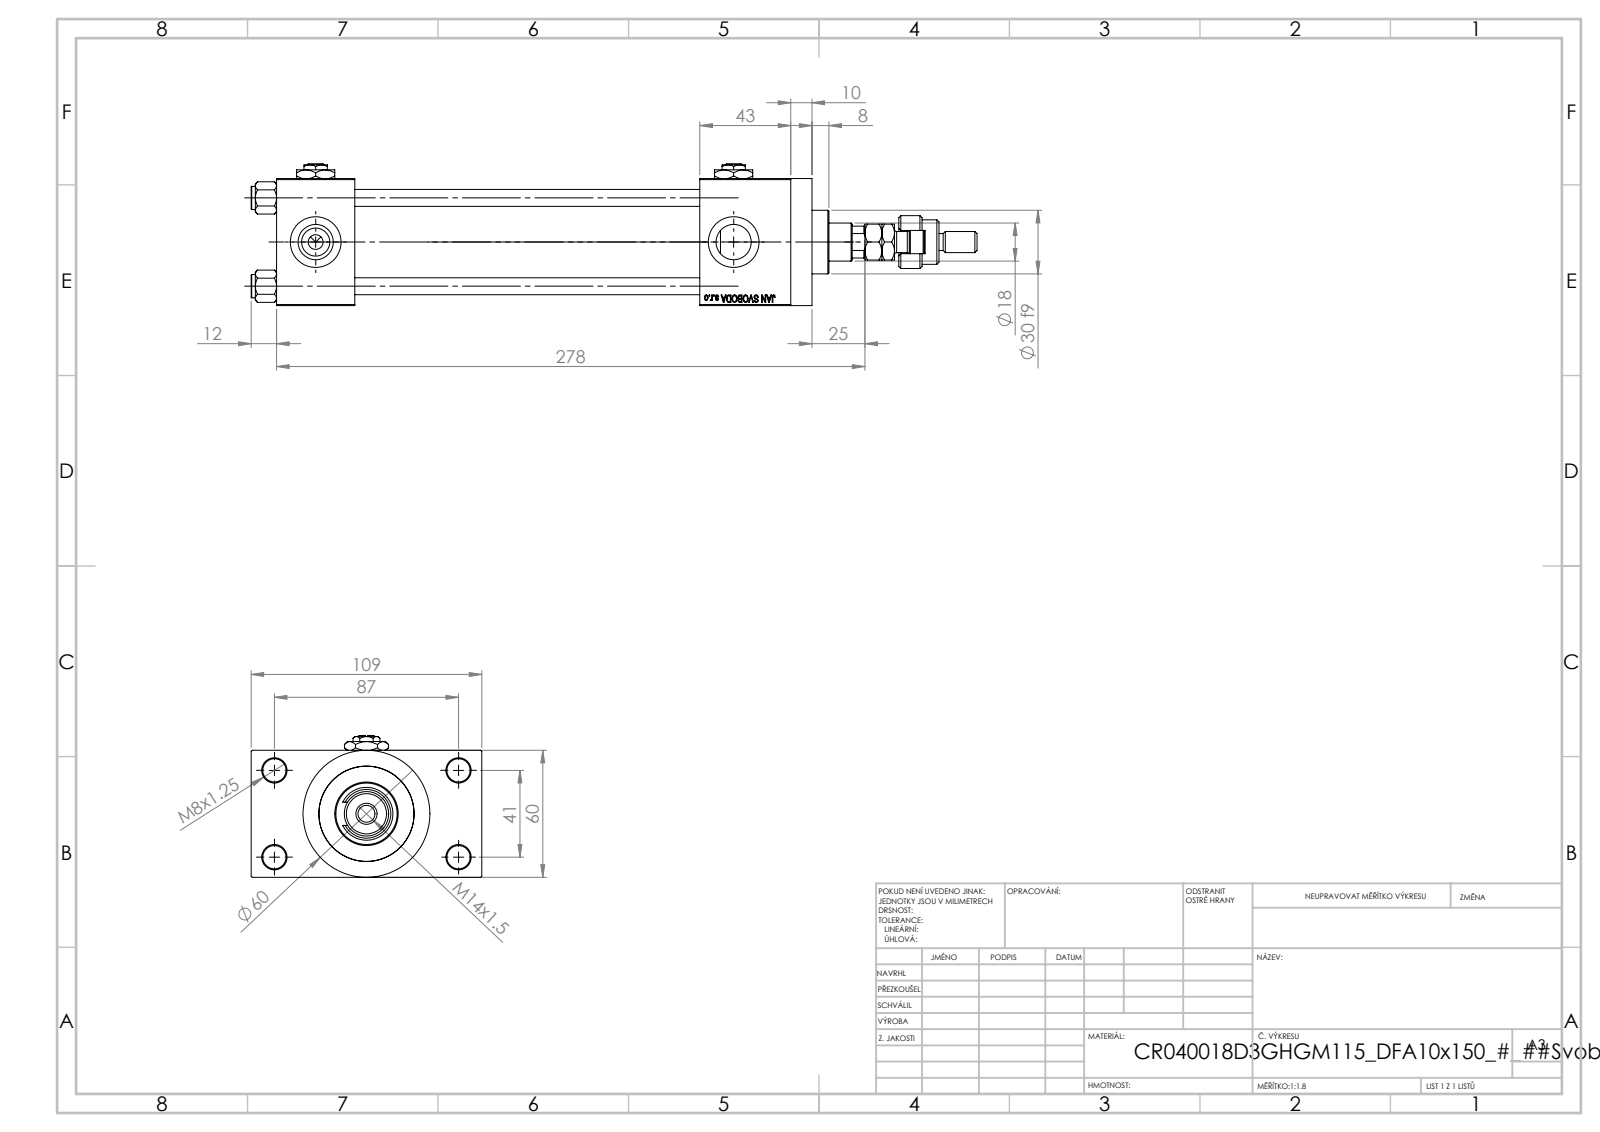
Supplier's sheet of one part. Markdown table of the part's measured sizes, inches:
| quantity | value |
| --- | --- |
| part name | Zatka_pro_OIL_PORT; V215CR_VCP_D; V215CR_D_TYCINKA; NUT_M5_D (+4 more) |
| STEP written by | SolidWorks 2019 (CONFIG_CONTROL_DESIGN) |
| units | inches |
| bodies | 15 solids, 1290 faces (574 planar, 112 cylindrical, 604 other) |
| overall size | 13.504 × 4.291 × 2.638 |
| volume | 37.38 in³ |
| surface area | 272 in² |
| round holes (diameter × count) | 0.315 × 4, 0.433 × 4, 0.656 × 4, 0.945 × 4, 0.276 × 3, 0.335 × 1, 0.709 × 1, 0.827 × 1, 1.22 × 1, 1.575 × 1, 1.772 × 1 |
| round bosses / shafts (diameter × count) | 0.433 × 4, 2.362 × 1, 1.811 × 1, 1.181 × 1, 0.984 × 1, 0.63 × 1, 0.394 × 1, 0.315 × 1 |
| partial cylindrical surfaces (radius × count) | 0.217 × 1, 0.335 × 1, 0.344 × 1 |
| main face-to-face distances | 2.362, 0.965, 6.417, 3.327, 1.457, 7.874, 1.693, 9.567, 8.11, 2.087 |
| hole center spacings | 0.892, 1.161, 1.642, 1.856, 1.893, 2.533, 3.011, 1.614 |
